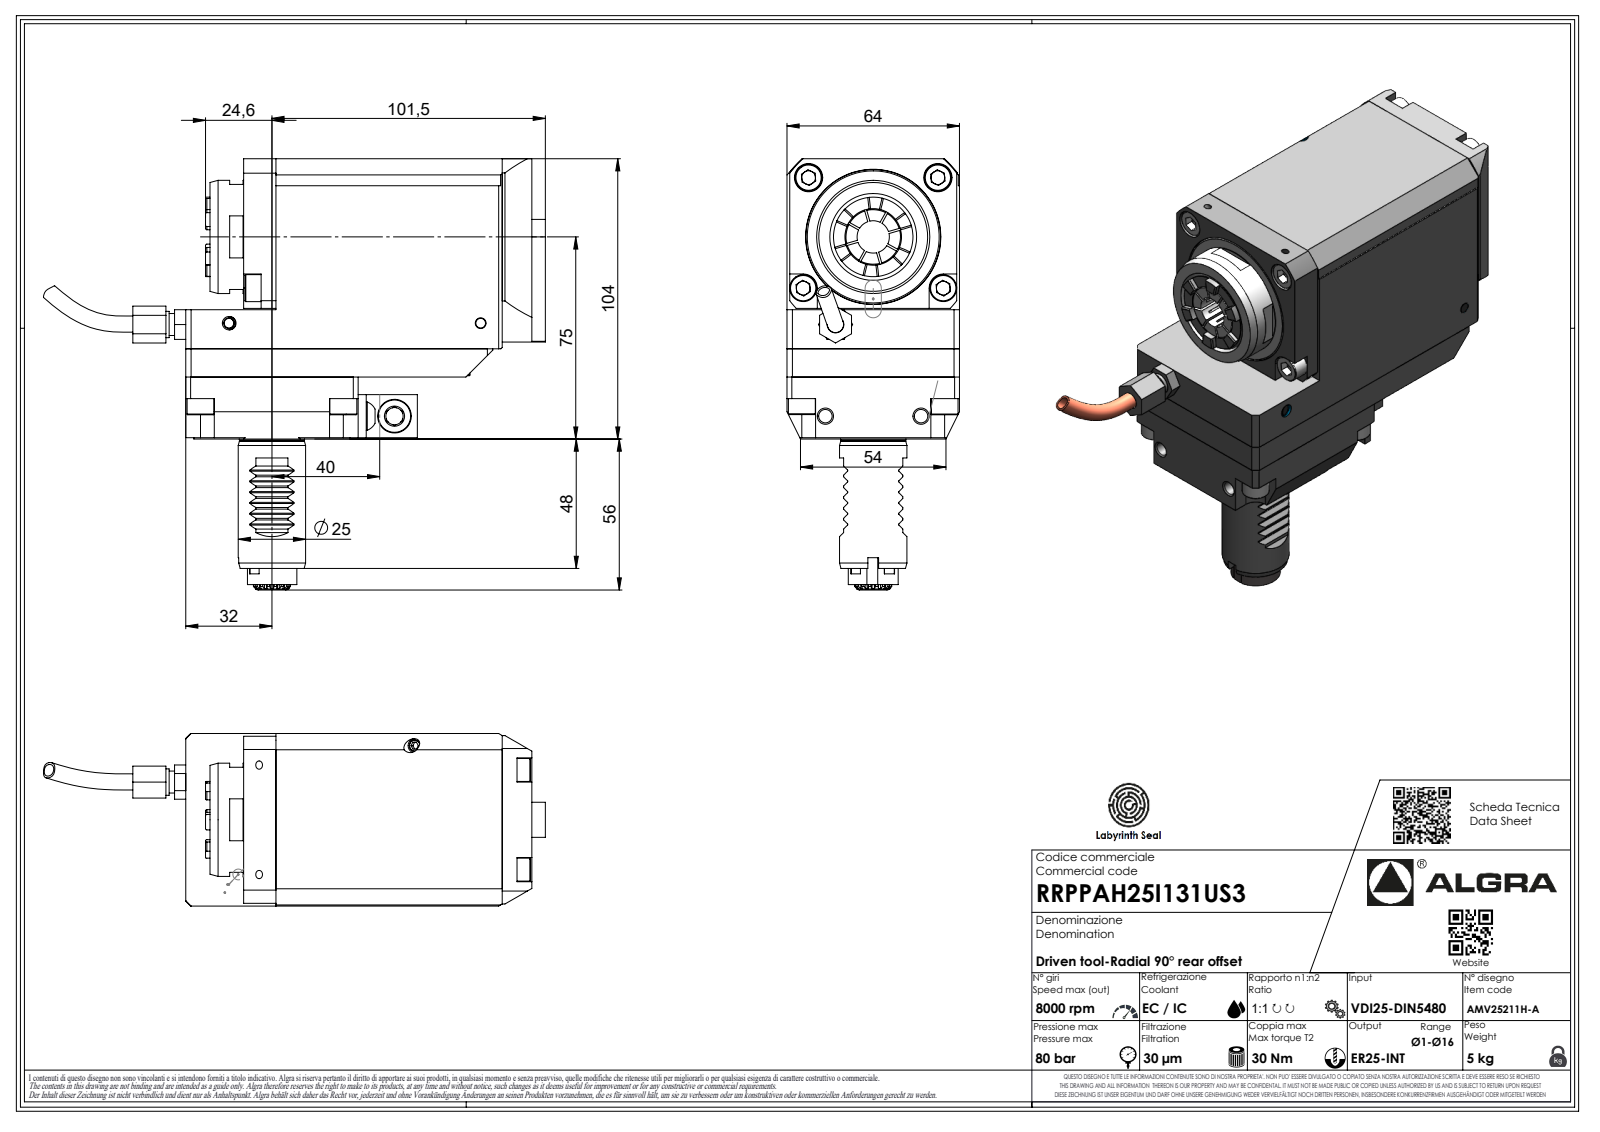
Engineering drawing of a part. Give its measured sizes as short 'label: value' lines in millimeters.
name: RRPPAH25I131US3
written by: SolidWorks 2023 (AUTOMOTIVE_DESIGN)
unit: mm
bodies: 1 solid, 778 faces (500 planar, 147 cylindrical, 131 other)
size: 186.31 × 160 × 64
volume: 699 988 mm³; area: 61 578 mm²
holes: 1× ⌀2.1, 1× ⌀22
bosses: 1× ⌀42, 1× ⌀25, 1× ⌀24.1, 1× ⌀18.5, 1× ⌀11, 1× ⌀9.8, 1× ⌀8.15, 1× ⌀6.37
rounds: 12× R0.3, 10× R35, 7× R0.33, 7× R0.52, 7× R3.7, 4× R5.1, 4× R5.25, 2× R4.5
face distances: 64, 48, 25, 128.5, 0.5, 81, 56, 104, 23, 107
